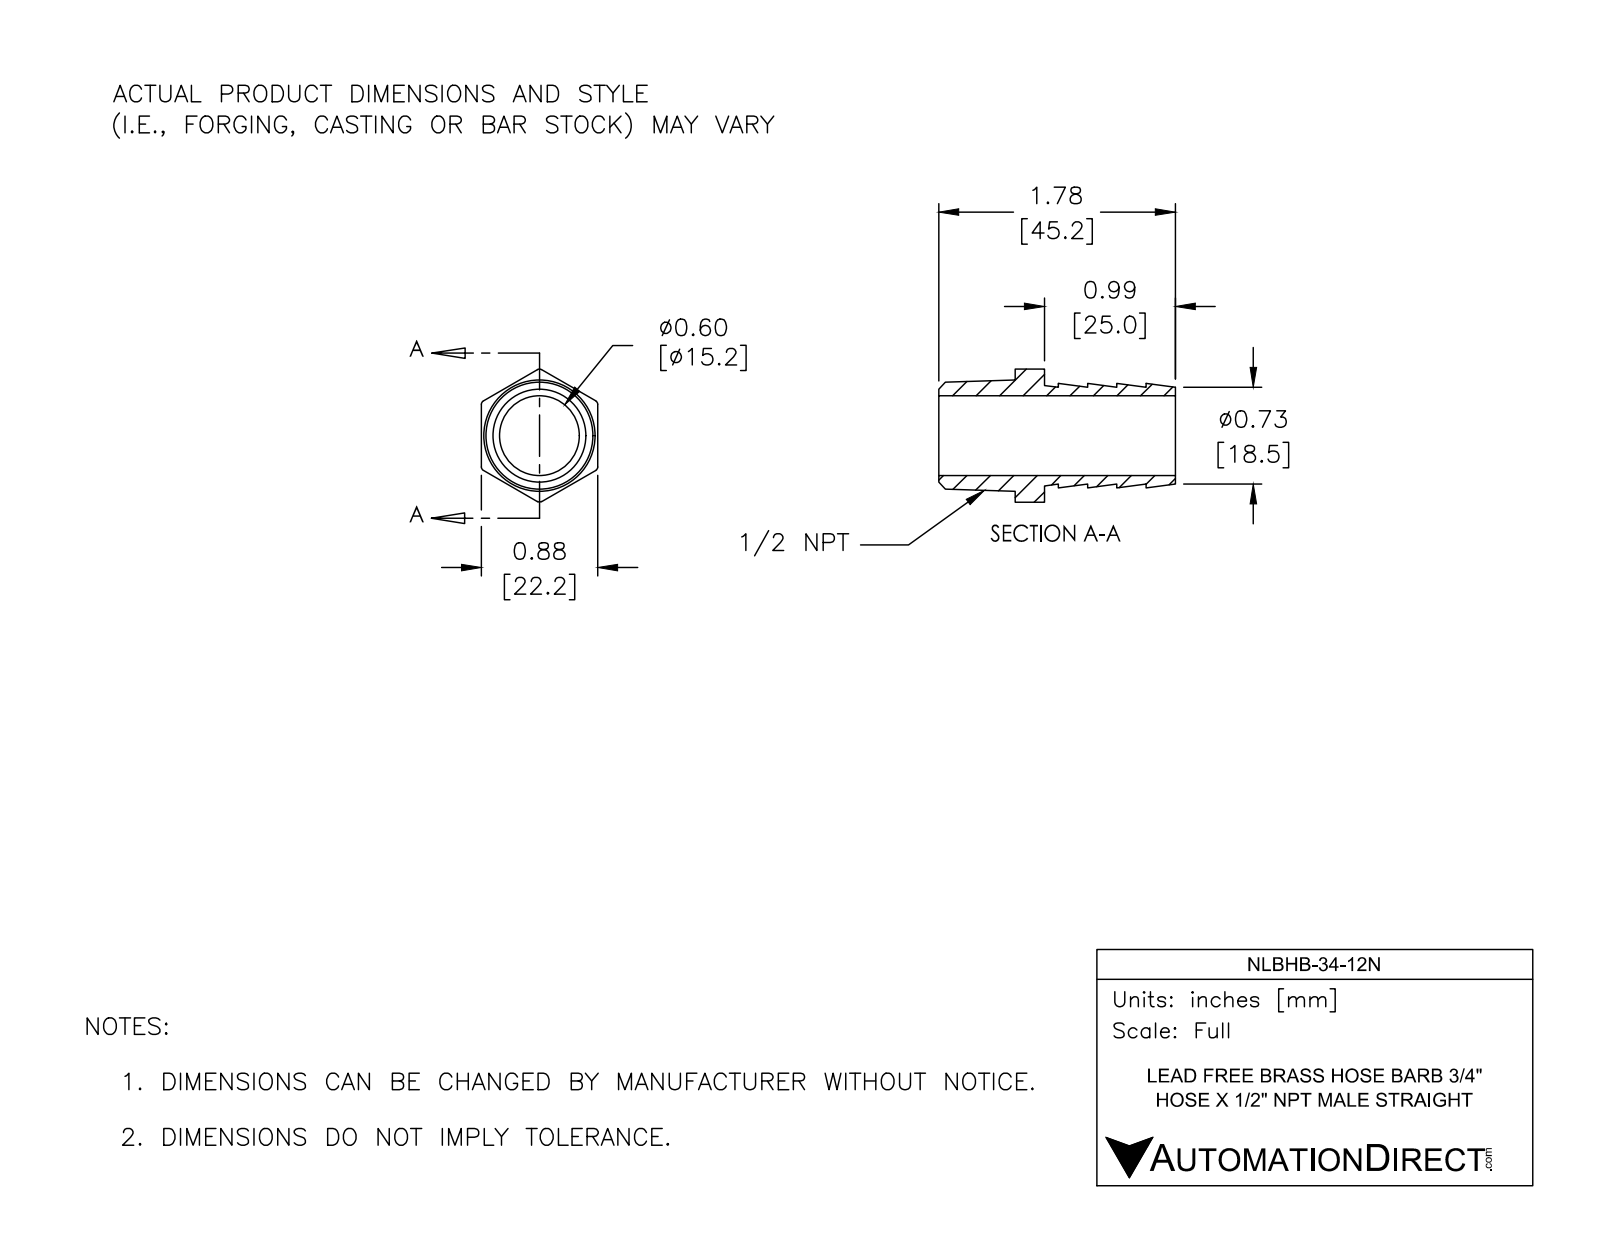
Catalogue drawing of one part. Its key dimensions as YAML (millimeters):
part_name: "NLBHB-34-12N"
step_written_by: "SolidWorks 2017 (AUTOMOTIVE_DESIGN)"
units: millimeters
bodies: {solids: 1, faces: 36, planar: 14, cylindrical: 8, other: 14}
overall_size: [45.2, 25.4, 22.2]
volume: 6290
surface_area: 5641
round_holes:
  - {diameter: 15.2, count: 1}
partial_cylinders:
  - {radius: 0.8, count: 6}
face_to_face_distances: [22.2, 5.6, 25, 5.6, 11.2, 30.6, 45.2, 20.2, 14.6, 11.2]
